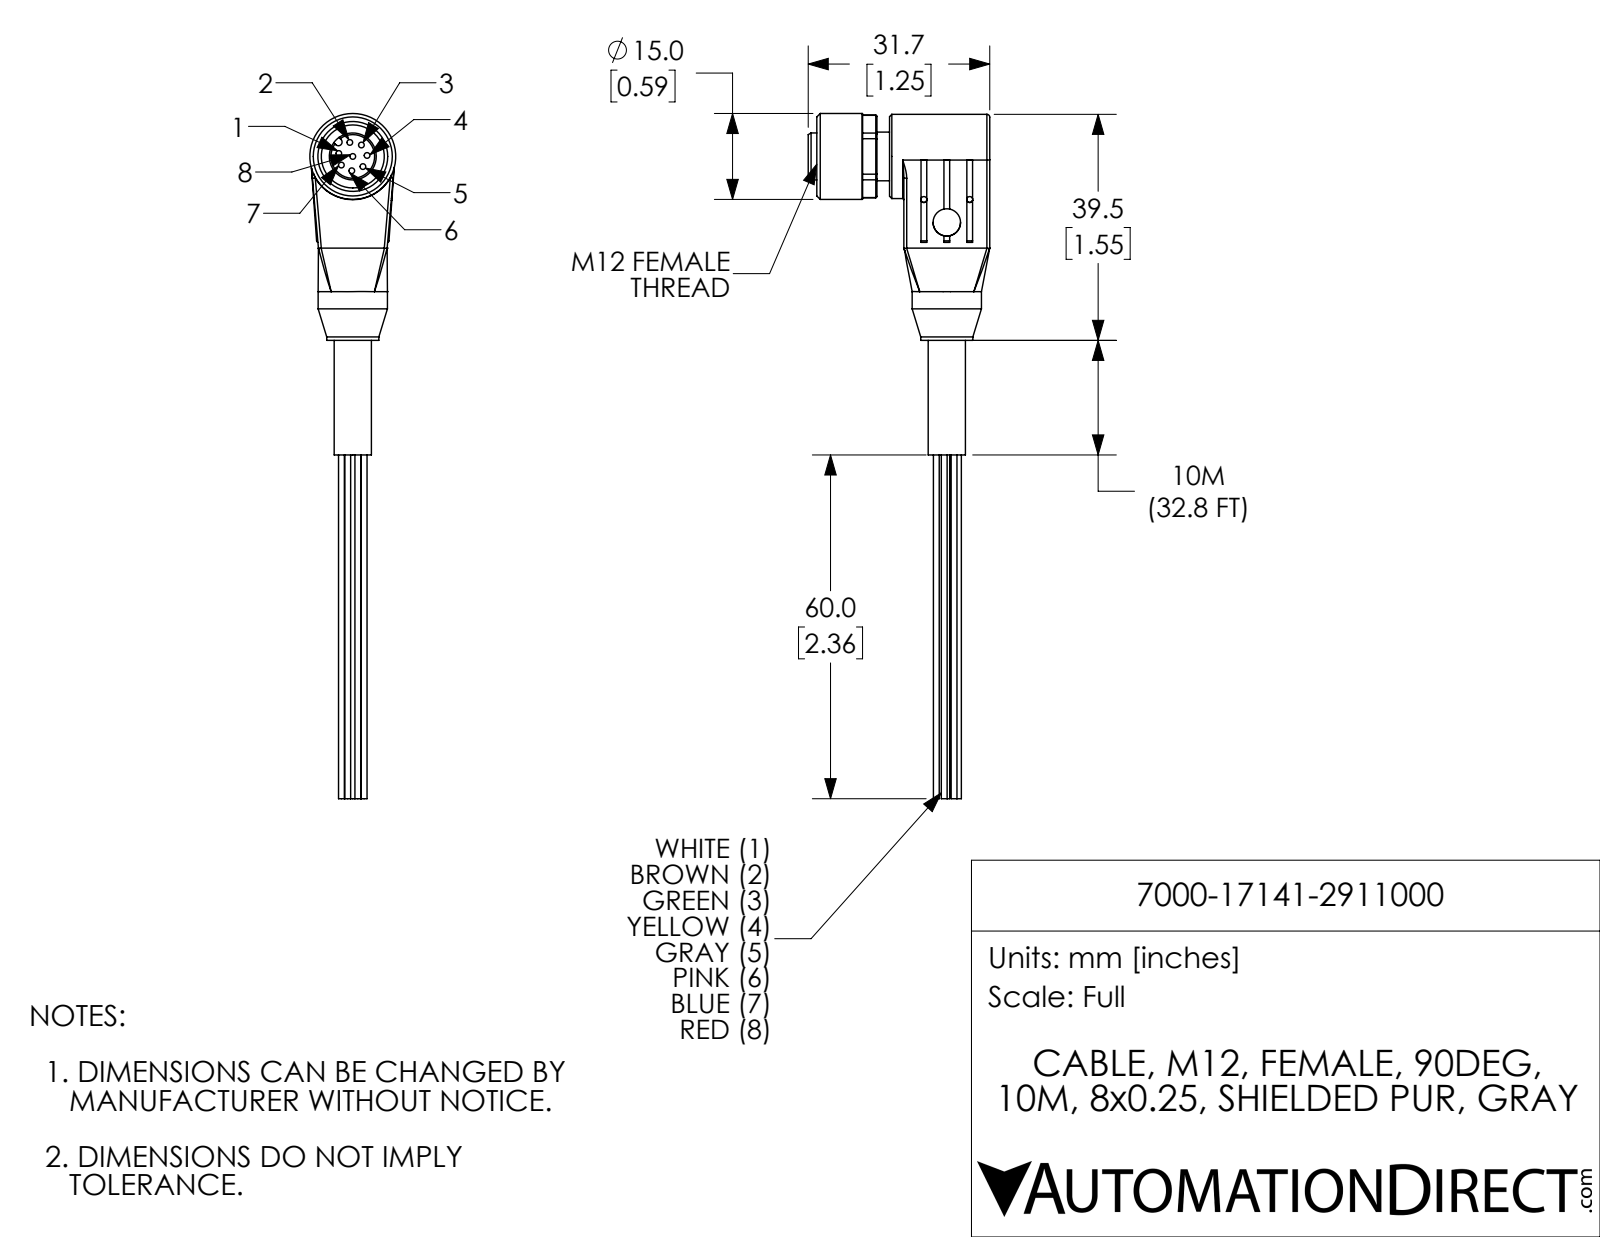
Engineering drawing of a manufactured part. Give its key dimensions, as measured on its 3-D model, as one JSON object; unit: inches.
{"part_name": "7000-17141-2911000", "step_written_by": "SolidWorks 2017 (AUTOMOTIVE_DESIGN)", "units": "inches", "bodies": {"solids": 1, "faces": 189, "planar": 81, "cylindrical": 75, "other": 33}, "overall_size": [4.709, 1.248, 0.591], "volume_in3": 0.579, "surface_area_in2": 8.705, "round_holes": [[0.039, 8], [0.041, 4], [0.189, 1], [0.433, 1]], "round_bosses_or_shafts": [[0.04, 8], [0.591, 1], [0.579, 1], [0.476, 1], [0.358, 1], [0.335, 1], [0.323, 1], [0.256, 1]], "partial_cylinders_radius": [[0.02, 4], [0.012, 2], [0.026, 1], [0.283, 1]], "face_to_face_distances": [0.098, 0.591, 0.185, 0.689, 0.776, 0.087, 0.118, 0.303, 0.472, 0.657], "hole_center_spacings": [0.098, 0.081, 0.149, 0.195, 0.082, 0.166, 0.189, 0.189]}
